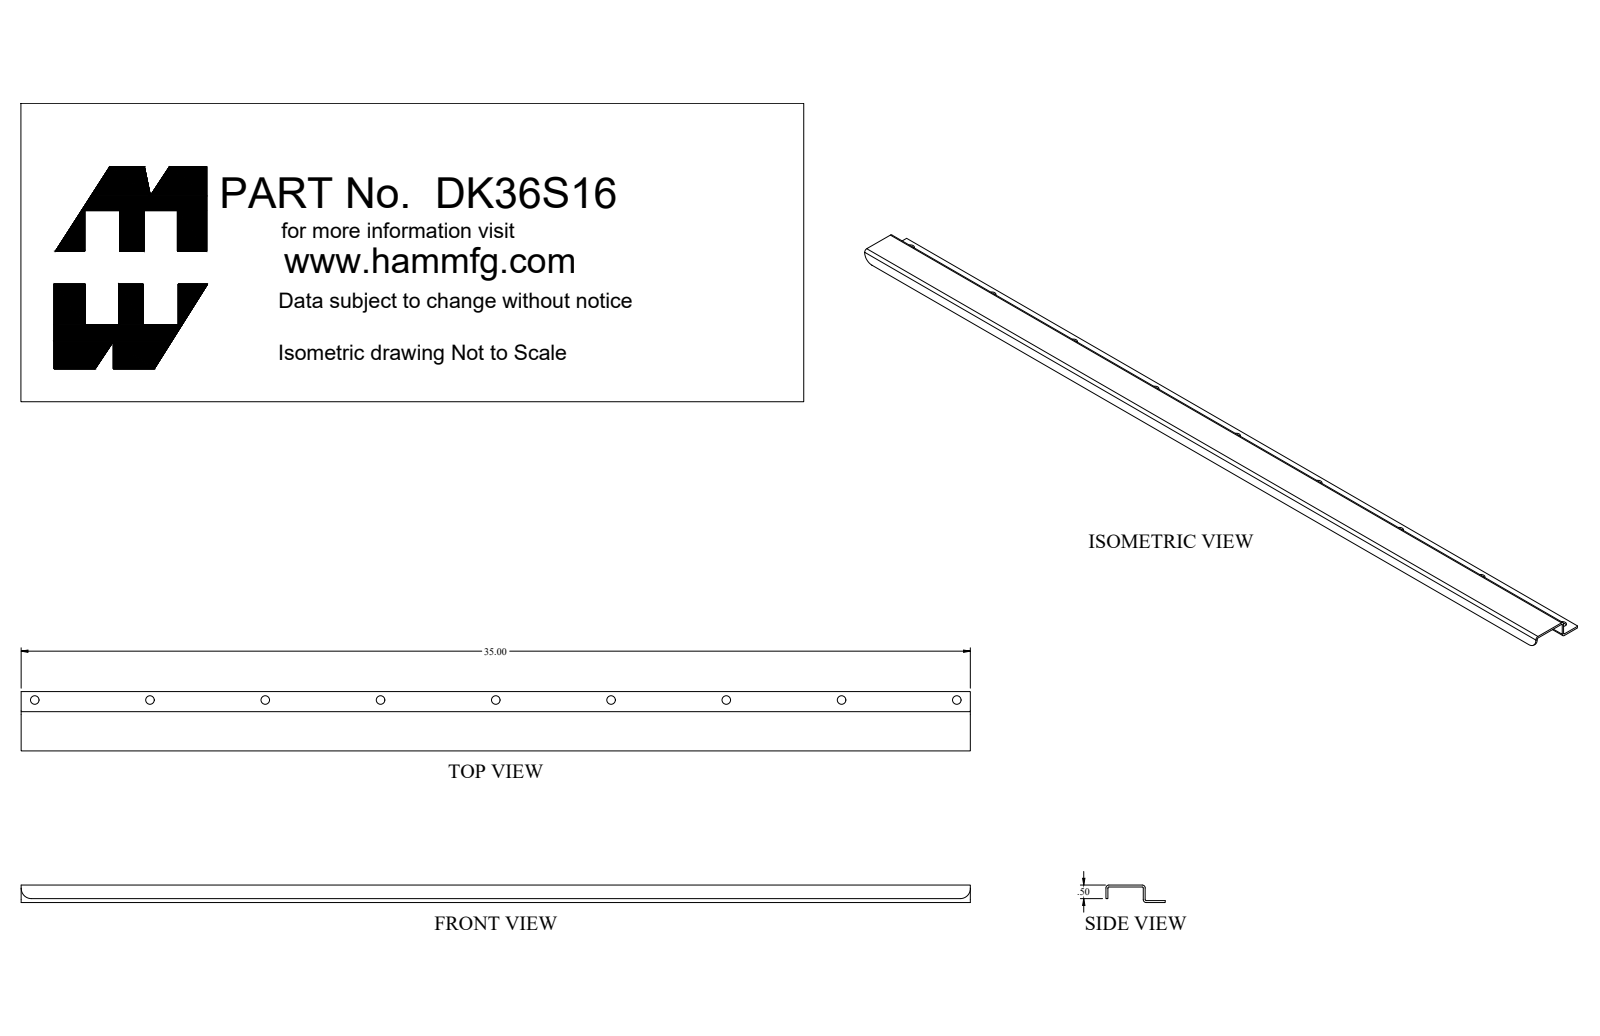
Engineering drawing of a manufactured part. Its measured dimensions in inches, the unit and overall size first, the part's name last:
Units: inches
Overall size (bounding box): 35 × 2.188 × 1.322
Round holes (diameter × count): ⌀0.313 ×9, ⌀0.201 ×1, ⌀0.275 ×1
Round bosses / shafts (diameter × count): ⌀0.625 ×1, ⌀0.483 ×1, ⌀0.25 ×1
Partial cylindrical surfaces — rounded edges, fillets, slot ends (radius × count): R0.036 ×3, R0.108 ×3, R0.375 ×2
Main face-to-face distances: 0.072, 0.572, 0.644, 1.376, 0.5, 0.063, 0.635, 0.707, 0.135, 1.448
Hole centre spacings: 4.25, 8.5, 12.75, 17, 21.25, 25.5, 29.75, 34
Volume: 9.511 in³ · Surface area: 280.9 in²
Bodies: 5 solids, 77 faces (35 planar, 36 cylindrical, 6 other)
Part name (STEP PRODUCT): DK36S16_Default
STEP written by: SolidWorks 2018 (CONFIG_CONTROL_DESIGN)
